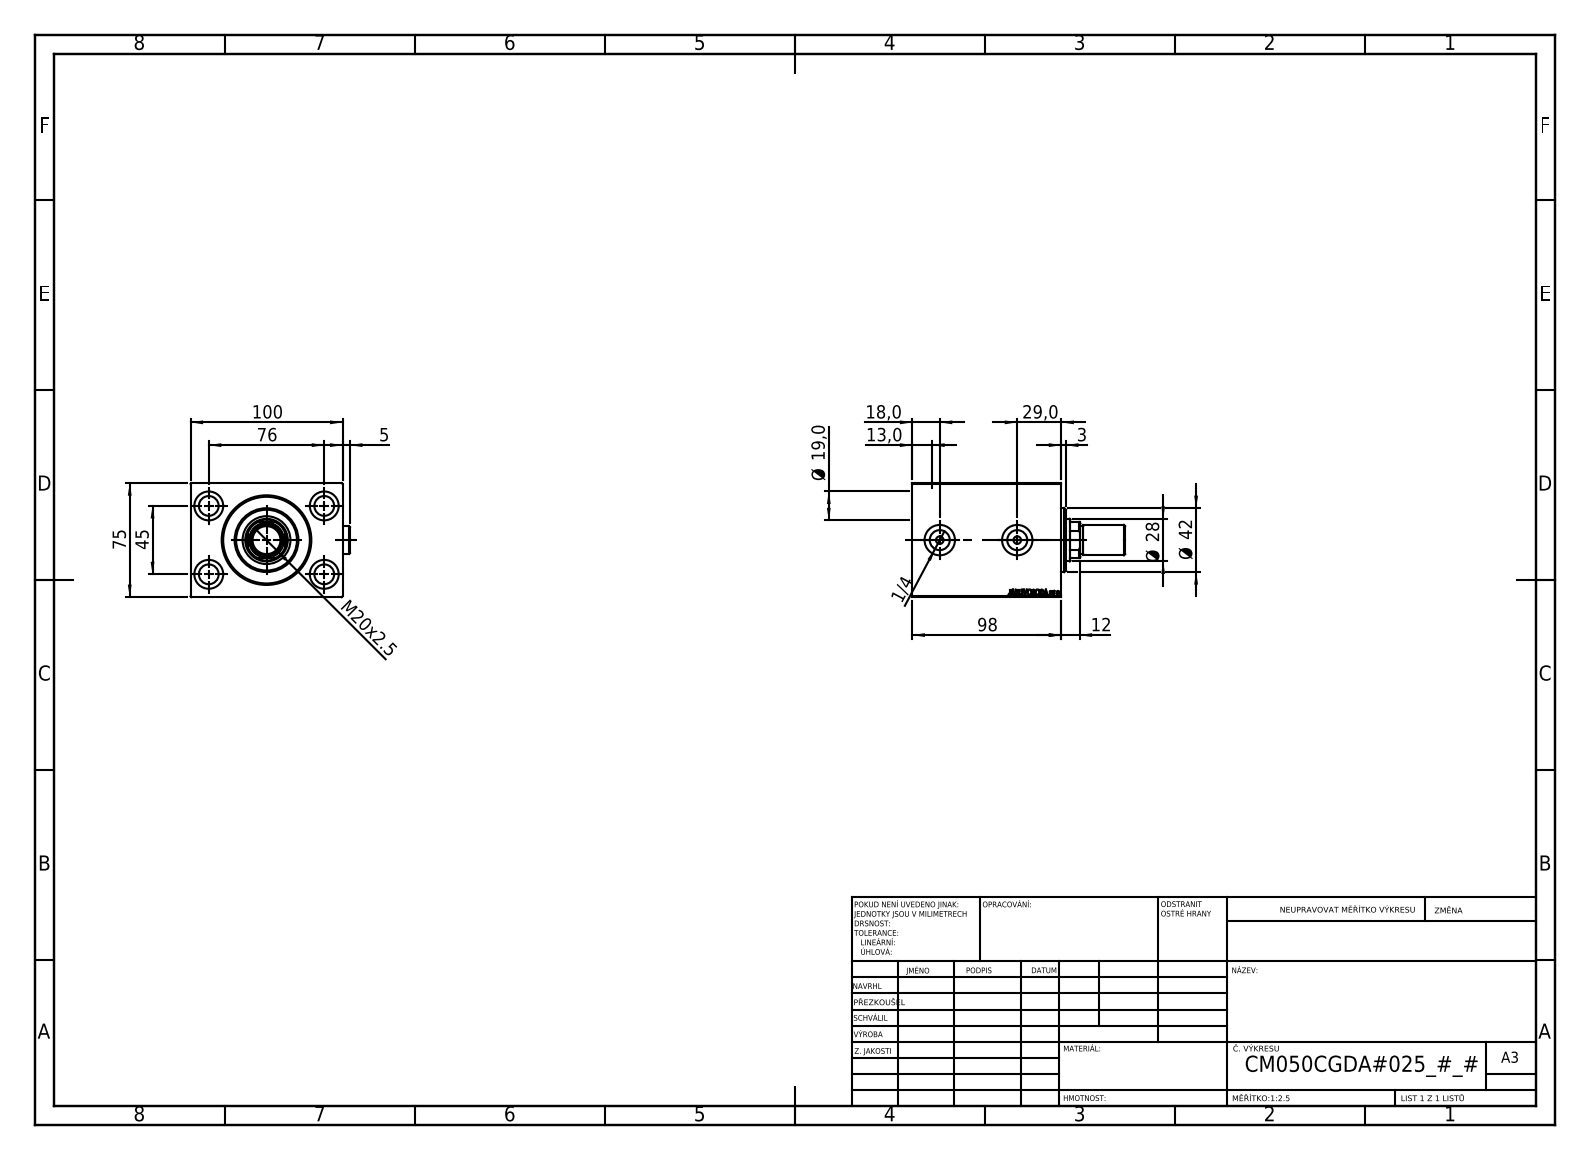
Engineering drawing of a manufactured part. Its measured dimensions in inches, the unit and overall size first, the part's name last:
Units: inches
Overall size (bounding box): 5.512 × 4.13 × 2.953
Round holes (diameter × count): ⌀0.512 ×4, ⌀0.748 ×4, ⌀0.197 ×2, ⌀0.518 ×2, ⌀0.787 ×2, ⌀0.728 ×1, ⌀1.102 ×1, ⌀1.24 ×1, ⌀1.969 ×1, ⌀2.047 ×1, ⌀2.244 ×1
Round bosses / shafts (diameter × count): ⌀0.709 ×3, ⌀1.654 ×1, ⌀0.787 ×1
Partial cylindrical surfaces — rounded edges, fillets, slot ends (radius × count): R0.531 ×1
Main face-to-face distances: 2.953, 3.937, 3.858, 0.551, 3.307, 0.472, 2.835, 0.984, 3.386, 1.85
Hole centre spacings: 1.739, 1.772, 2.992, 3.477, 2.008
Volume: 38.97 in³ · Surface area: 172.5 in²
Bodies: 6 solids, 933 faces (447 planar, 82 cylindrical, 404 other)
Part name (STEP PRODUCT): V450CM_C_VCP; V450CM_VC_B; V450CM_C_Body; V450CM_MALE_METRIC (+1 more)
STEP written by: SolidWorks 2019 (CONFIG_CONTROL_DESIGN)
